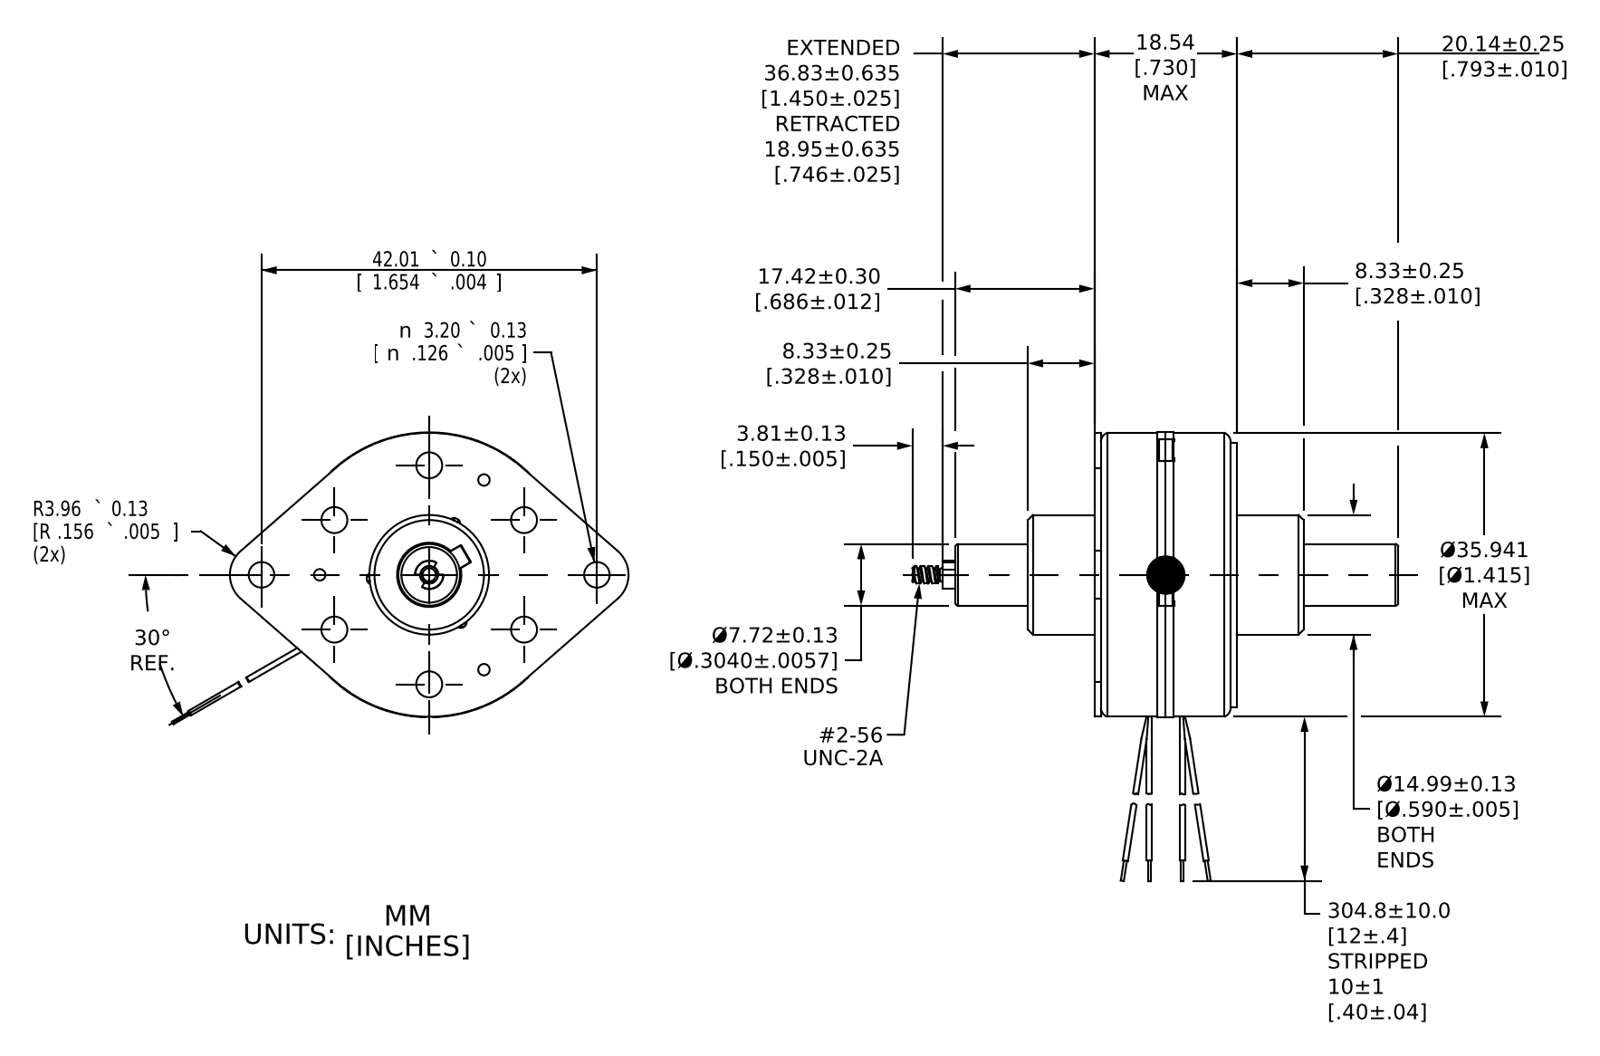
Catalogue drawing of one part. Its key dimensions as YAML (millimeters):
part_name: "149-6054-002_1; MANIFOLD_SOLID_BREP_2307; MANIFOLD_SOLID_BREP_2630; 053-0117-001_2_ASM (+8 more)"
step_written_by: "PRO/ENGINEER BY PARAMETRIC TECHNOLOGY CORPORATION, 2014310 (CONFIG_CONTROL_DESIGN)"
units: millimeters
bodies: {solids: 18, faces: 456, planar: 169, cylindrical: 213, other: 74}
overall_size: [59.7, 49.9, 35.9]
volume: 26430
surface_area: 21900
round_holes:
  - {diameter: 3.3, count: 7}
  - {diameter: 2.6, count: 4}
  - {diameter: 3.5, count: 4}
  - {diameter: 3.2, count: 2}
  - {diameter: 3.3, count: 2}
  - {diameter: 5.5, count: 1}
  - {diameter: 8.1, count: 1}
  - {diameter: 14.1, count: 1}
  - {diameter: 18.4, count: 1}
  - {diameter: 19.7, count: 1}
  - {diameter: 34.1, count: 1}
  - {diameter: 34.3, count: 1}
round_bosses_or_shafts:
  - {diameter: 3.5, count: 4}
  - {diameter: 1.1, count: 4}
  - {diameter: 35.9, count: 1}
  - {diameter: 35.7, count: 1}
  - {diameter: 34.3, count: 1}
  - {diameter: 33.1, count: 1}
  - {diameter: 33.1, count: 1}
  - {diameter: 17.8, count: 1}
partial_cylinders:
  - {radius: 0.6, count: 8}
  - {radius: 0.8, count: 6}
  - {radius: 1, count: 4}
  - {radius: 1.4, count: 4}
  - {radius: 0.1, count: 2}
  - {radius: 2, count: 2}
  - {radius: 4, count: 2}
  - {radius: 1.2, count: 1}
face_to_face_distances: [8.1, 0.8, 8.9, 7.3, 17.1, 16.3, 9.8, 1.6, 15.1, 17.9]
hole_center_spacings: [13.7, 23.7, 25.8, 6.9, 7, 11.4, 13, 18.9]
